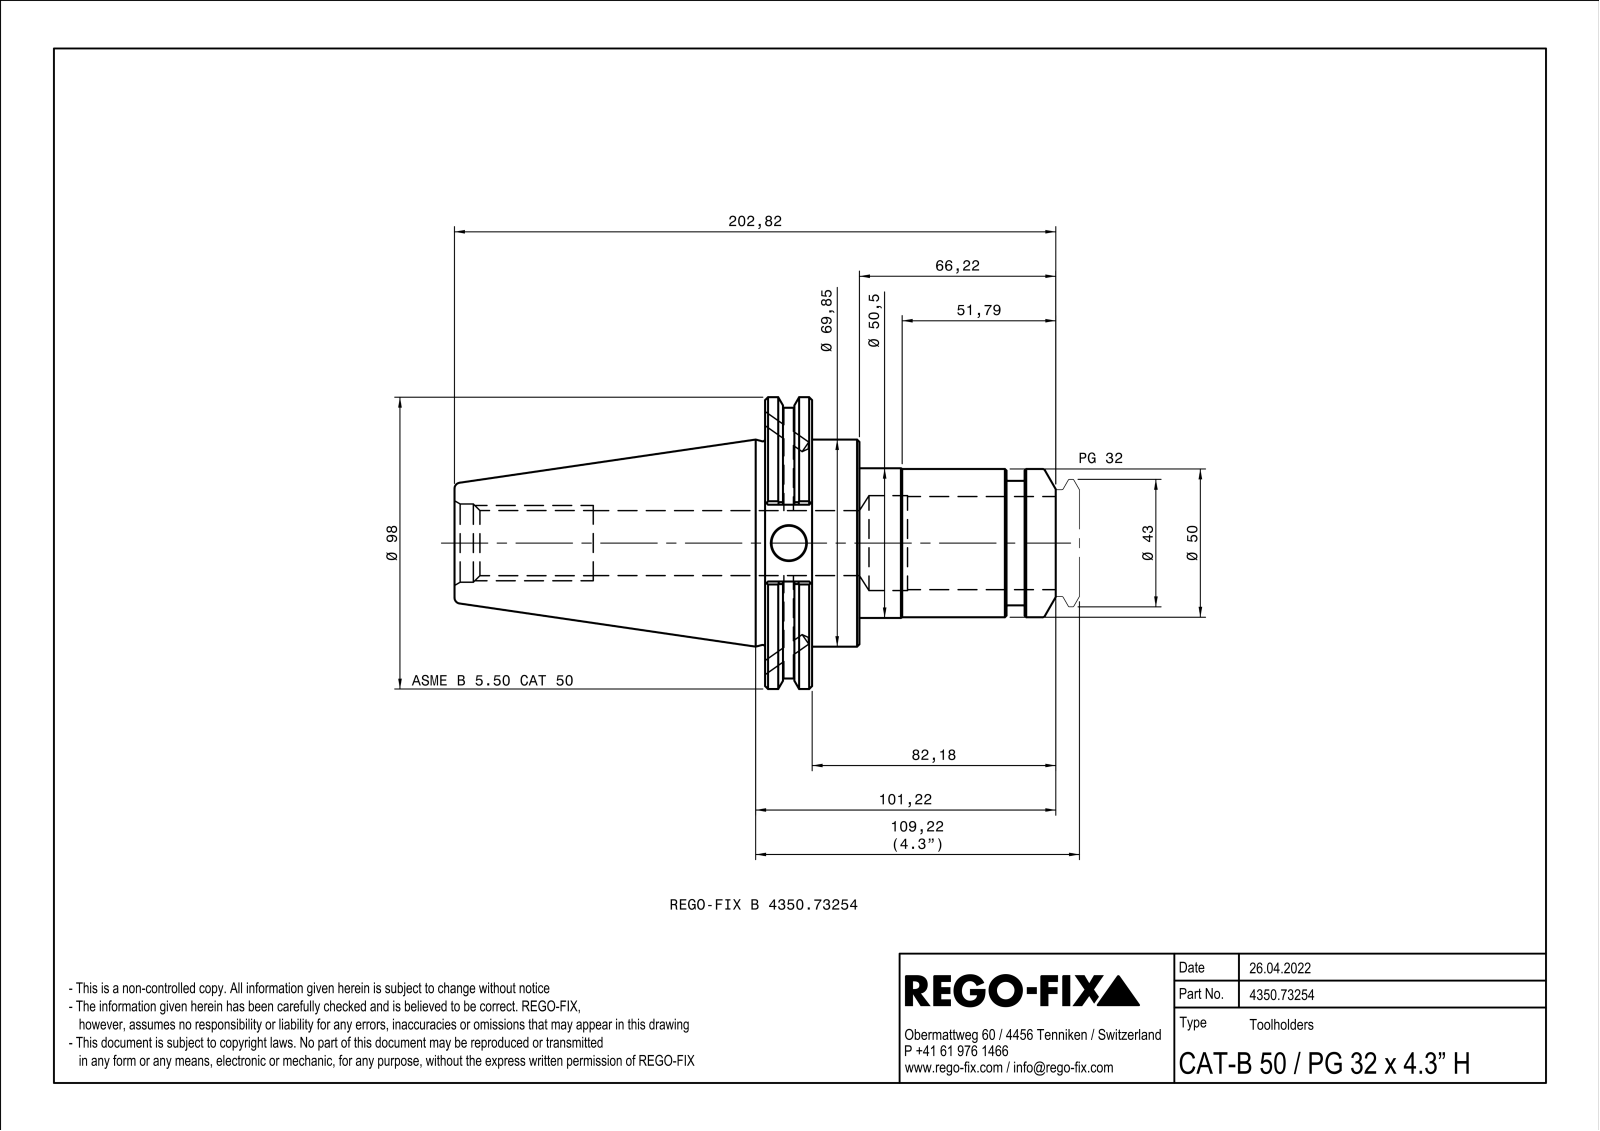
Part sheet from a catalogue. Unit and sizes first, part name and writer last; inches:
Units: inches
Overall size (bounding box): 7.985 × 3.875 × 3.716
Round holes (diameter × count): ⌀0.461 ×1, ⌀0.865 ×1, ⌀1.039 ×1, ⌀1.299 ×1
Round bosses / shafts (diameter × count): ⌀3.875 ×1, ⌀3.594 ×1, ⌀2.75 ×1, ⌀1.988 ×1, ⌀1.969 ×1, ⌀1.654 ×1
Partial cylindrical surfaces — rounded edges, fillets, slot ends (radius × count): R0.02 ×12
Main face-to-face distances: 0.625, 0.628, 1.253, 1.954, 2.582, 3.207, 0.24, 2.194, 2.822, 3.447
Volume: 27.12 in³ · Surface area: 101.7 in²
Bodies: 1 solid, 114 faces (34 planar, 30 cylindrical, 50 other)
Part name (STEP PRODUCT): NOCUT
STEP written by: SIEMENS PLM Software Solid Edge ST10 (AUTOMOTIVE_DESIGN)
